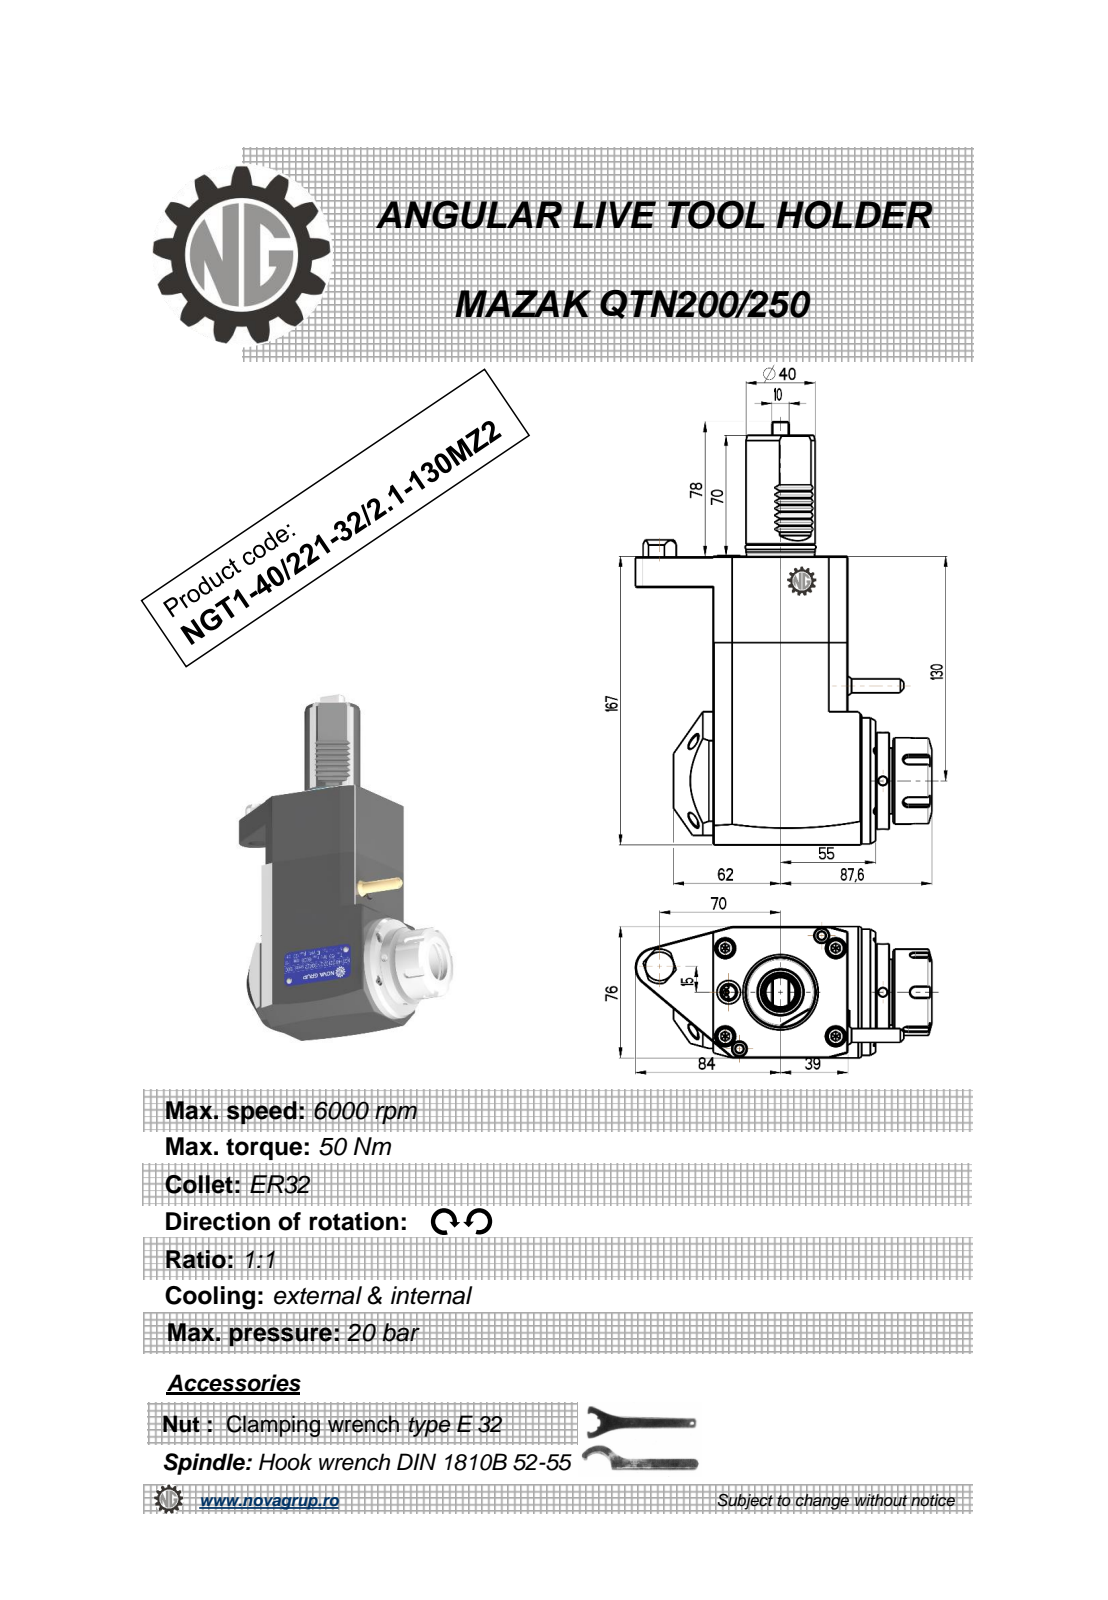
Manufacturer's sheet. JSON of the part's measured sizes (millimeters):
{"part_name": "NGT1_40_221_32_2_1_130MZ2", "step_written_by": "PRO/ENGINEER BY PARAMETRIC TECHNOLOGY CORPORATION, 2010280 (CONFIG_CONTROL_DESIGN)", "units": "millimeters", "bodies": {"solids": 1, "faces": 289, "planar": 132, "cylindrical": 74, "other": 83}, "overall_size": [245, 171.6, 76], "volume_mm3": 1296000, "surface_area_mm2": 92403, "round_holes": [[5, 3], [3, 1], [8, 1], [27, 1]], "round_bosses_or_shafts": [[73, 1], [56, 1], [50, 1], [43, 1], [40, 1], [39.4, 1], [36.2, 1], [10, 1]], "partial_cylinders_radius": [[0.3, 7], [0.2, 6], [3, 5], [0.8, 2], [300, 2], [9, 1], [10, 1], [11.35, 1]], "face_to_face_distances": [76, 78, 167, 8, 16, 94, 18, 87.92, 149, 86], "hole_center_spacings": [60.42, 89.25]}
